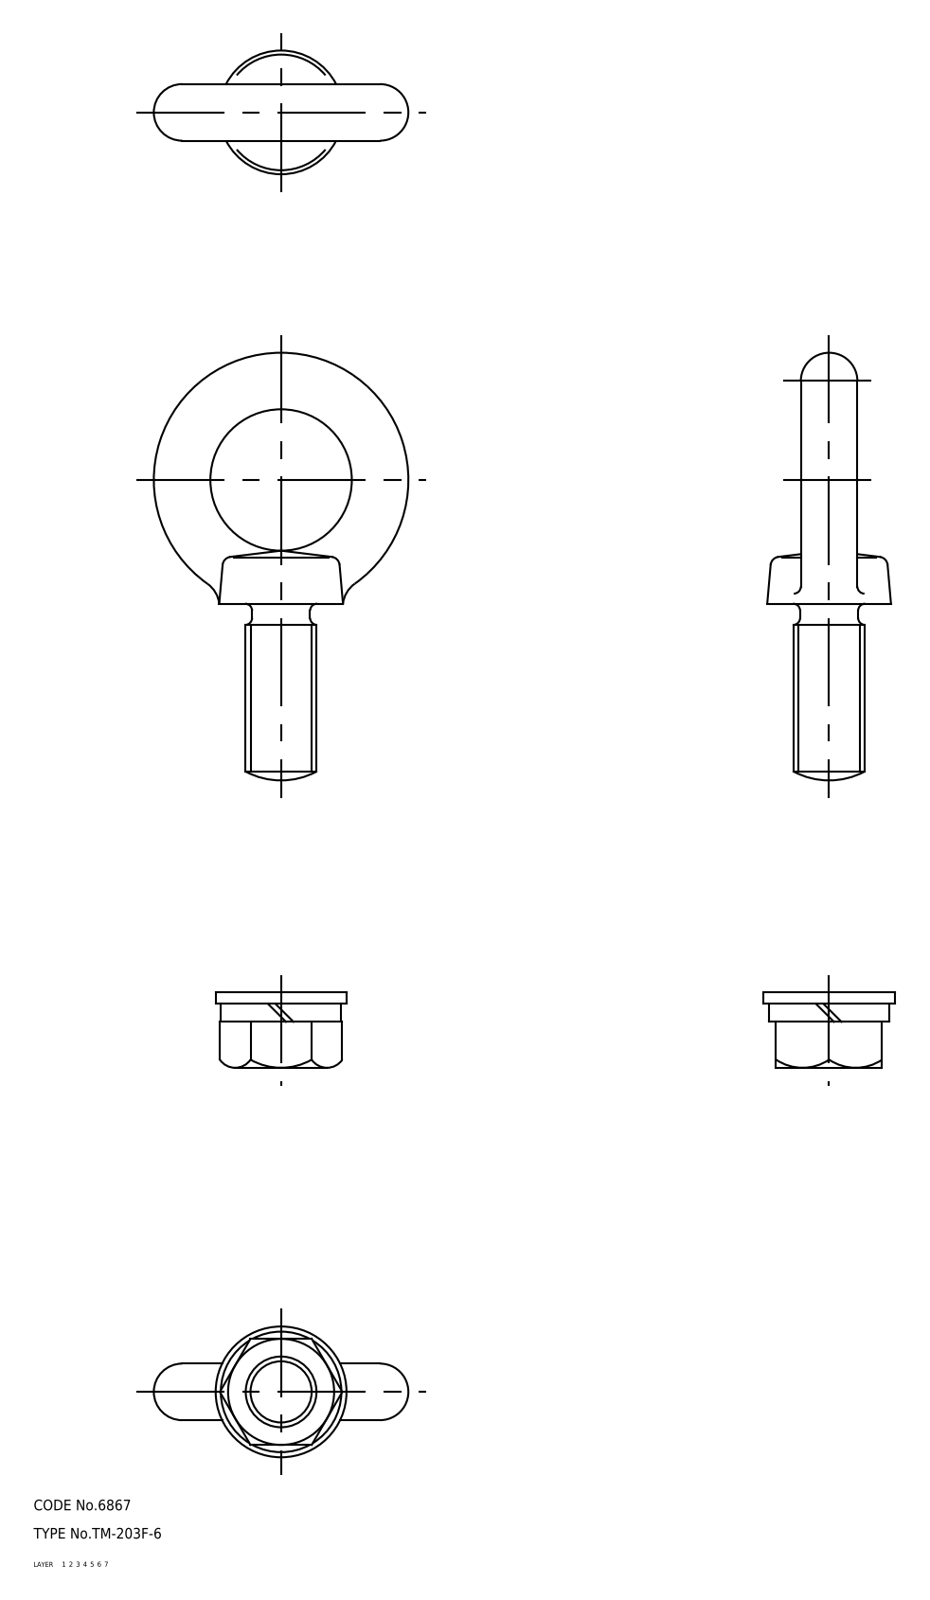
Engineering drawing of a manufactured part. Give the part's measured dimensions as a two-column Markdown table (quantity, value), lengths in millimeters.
| quantity | value |
| --- | --- |
| part name | TM_203F_6 |
| STEP written by | SolidWorks 2003240 (AUTOMOTIVE_DESIGN) |
| units | millimeters |
| bodies | 4 solids, 56 faces (13 planar, 12 cylindrical, 31 other) |
| overall size | 121 × 72 × 37 |
| volume | 68 817 mm³ |
| surface area | 20 348 mm² |
| round holes (diameter × count) | 20 × 1 |
| round bosses / shafts (diameter × count) | 37 × 1, 34.1 × 1 |
| main face-to-face distances | 3.2, 5.1, 8.3, 30, 13, 18.1, 21.3 |
